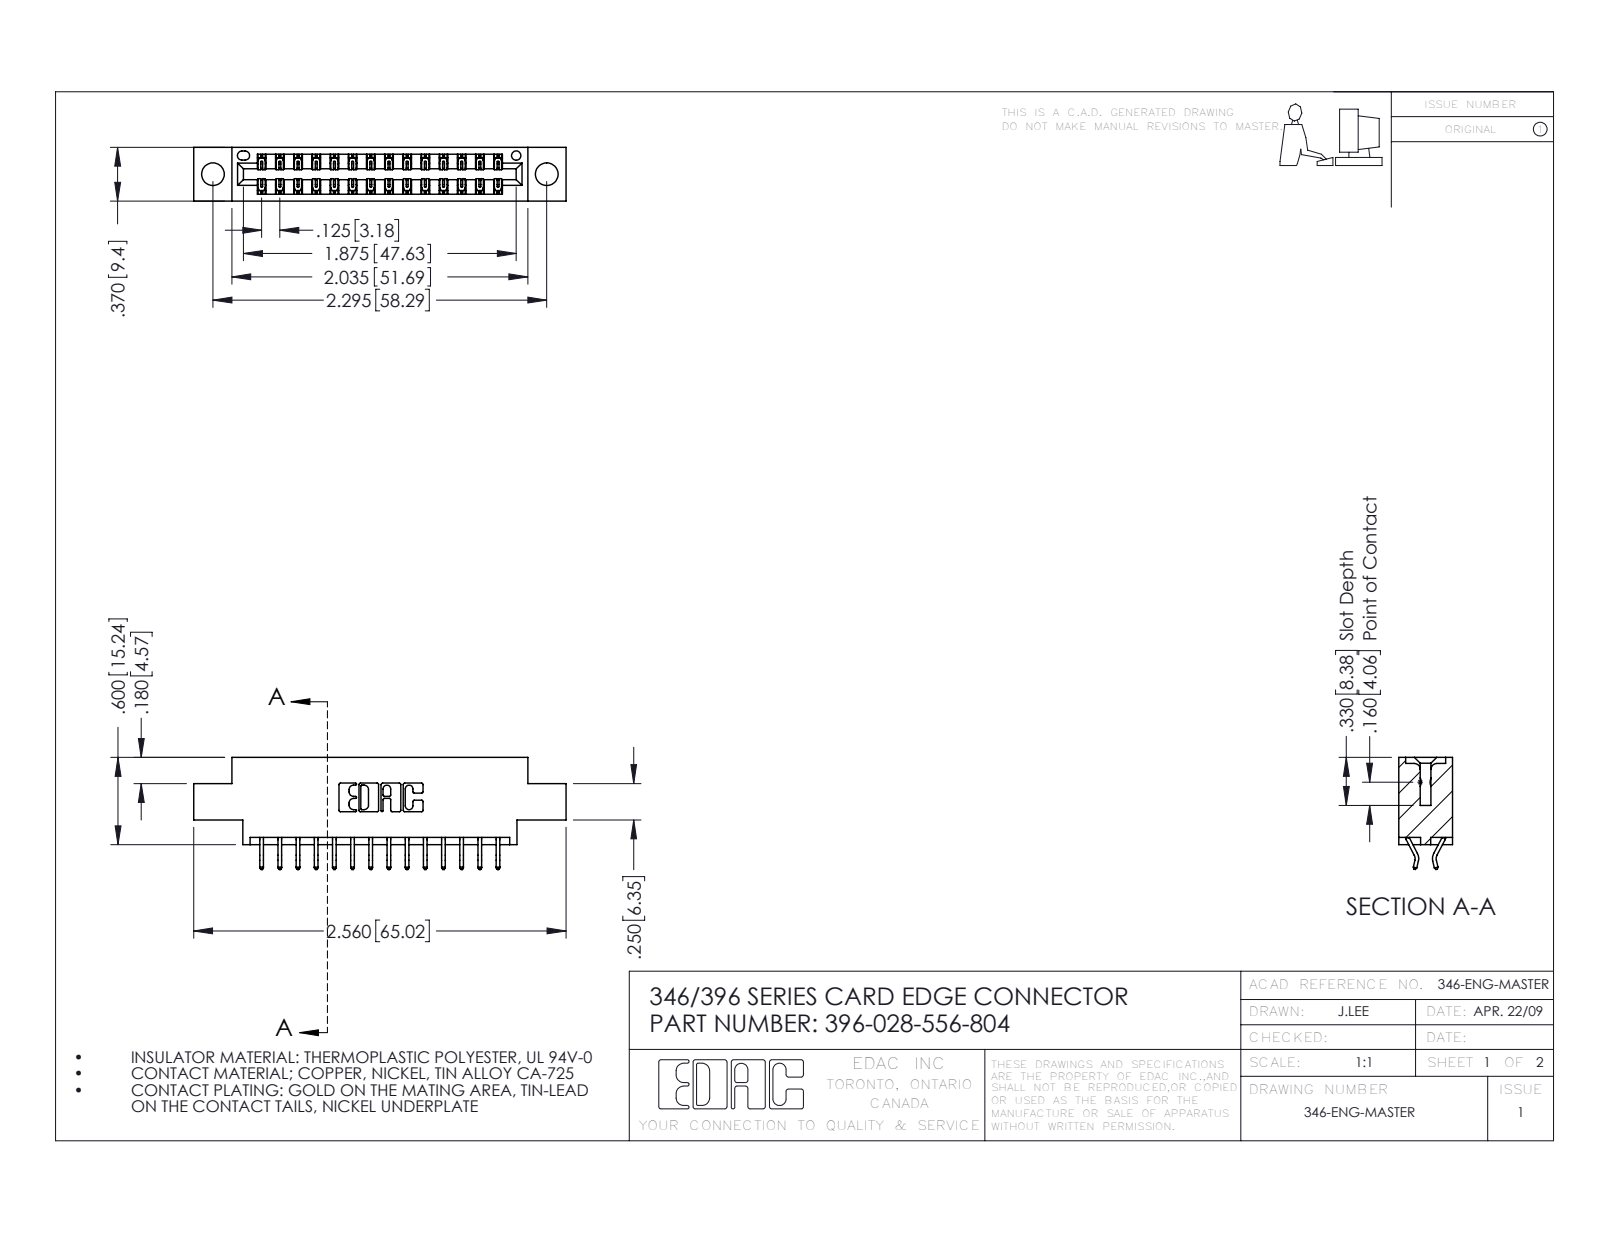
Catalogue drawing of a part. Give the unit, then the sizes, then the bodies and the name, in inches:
Units: inches
Overall size (bounding box): 2.56 × 0.77 × 0.37
Round holes (diameter × count): ⌀0.156 ×2, ⌀0.064 ×1
Partial cylindrical surfaces — rounded edges, fillets, slot ends (radius × count): R0.006 ×42, R0.01 ×22, R0.007 ×6, R0.031 ×6, R0.026 ×3, R0.01 ×2, R0.014 ×2, R0.022 ×2
Main face-to-face distances: 0.048, 0.322, 0.37, 0.25, 0.025, 0.072, 0.298, 0.275, 0.148, 0.222
Hole centre spacings: 0.246, 2.089, 2.295
Volume: 0.359 in³ · Surface area: 11.79 in²
Bodies: 29 solids, 1750 faces (1172 planar, 578 cylindrical, 0 other)
Part name (STEP PRODUCT): 345-292-001_556 Tail; 396-028-556-804; 346 Part_0.170 Offset - 0.156 Dia-TH
STEP written by: SolidWorks 2016 (CONFIG_CONTROL_DESIGN)
